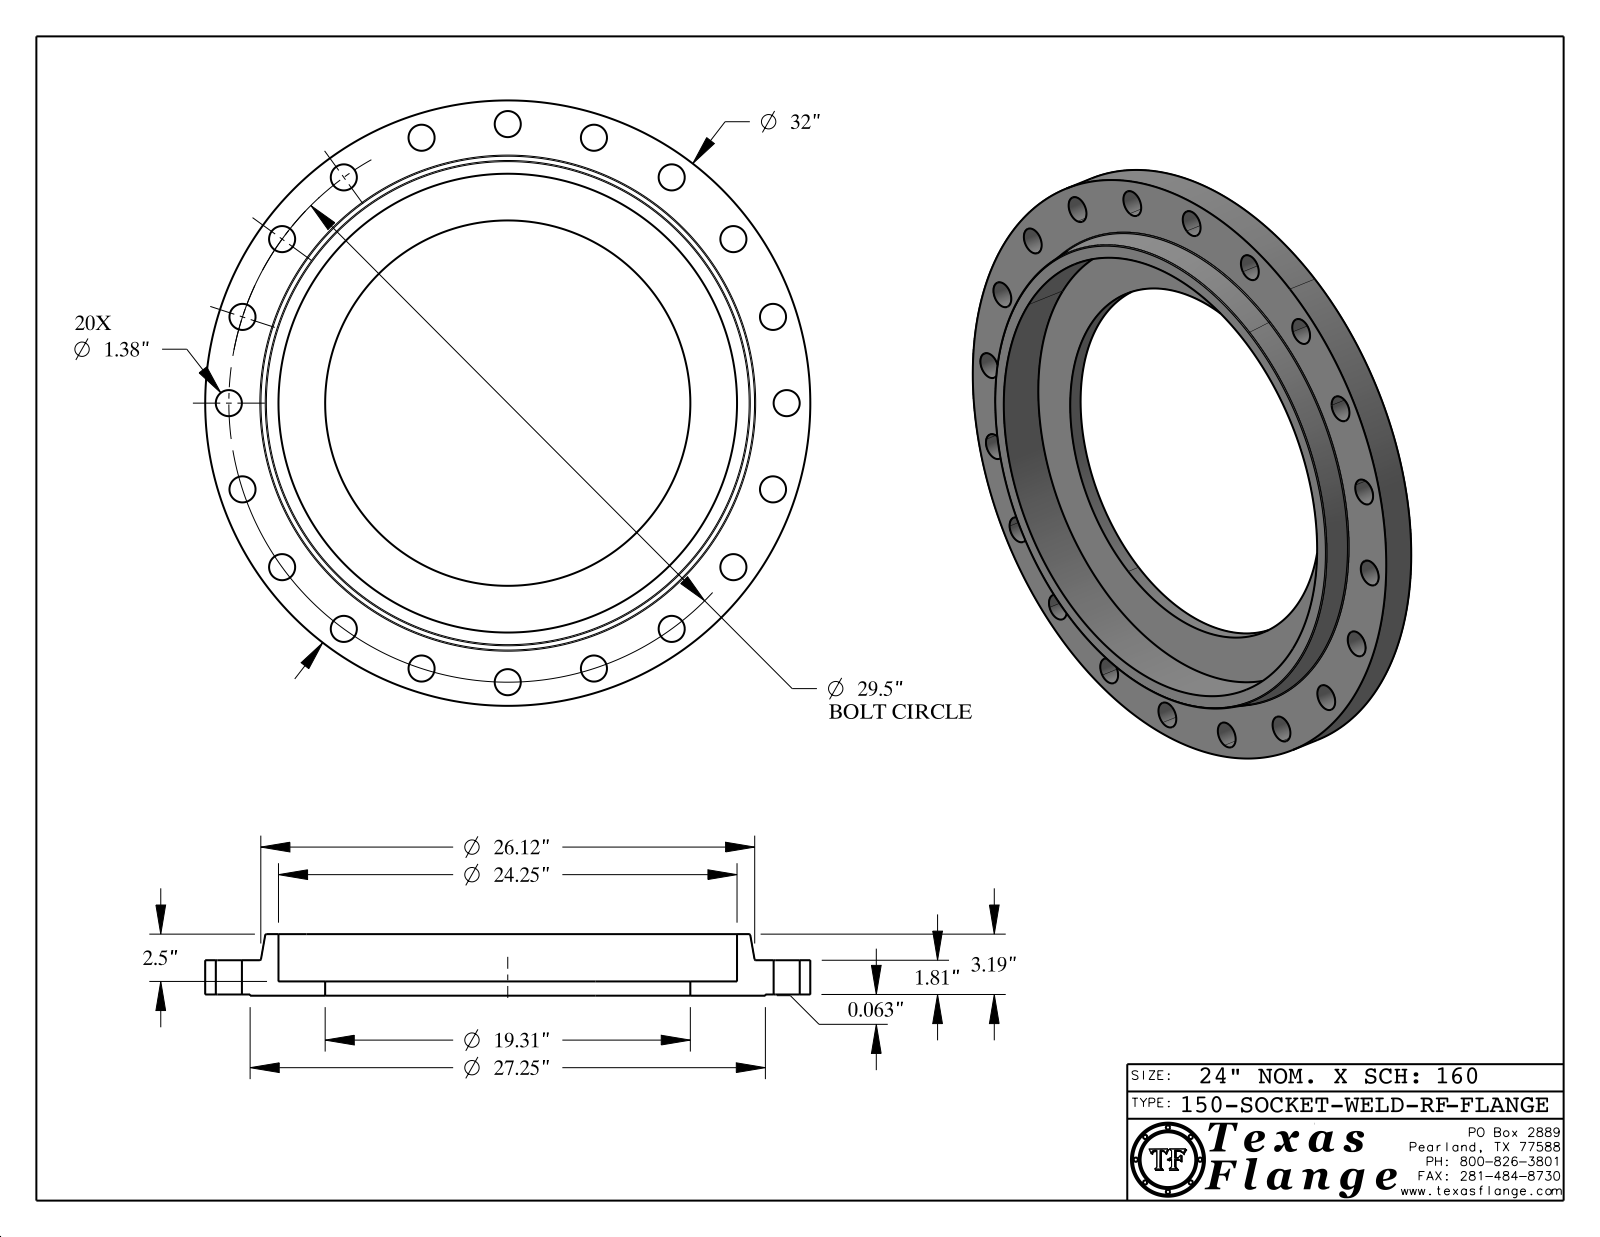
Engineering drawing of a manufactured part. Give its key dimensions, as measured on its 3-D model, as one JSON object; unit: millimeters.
{"part_name": "150-SOCKET-WELD-RF", "step_written_by": "CATIA V5 STEP AP214 (AUTOMOTIVE_DESIGN)", "units": "millimeters", "bodies": {"solids": 1, "faces": 444, "planar": 370, "cylindrical": 68, "other": 6}, "overall_size": [812.8, 812.8, 82.6], "volume_mm3": 12920000, "surface_area_mm2": 1055000, "round_holes": [[35.1, 20], [12.6, 1], [490.5, 1], [616, 1]], "round_bosses_or_shafts": [[0.8, 8], [812.8, 1], [692.2, 1], [9.9, 1]], "face_to_face_distances": [47.5, 1.6, 46, 19.1, 17.5, 28.4, 82.6, 81, 63.5, 35.1], "hole_center_spacings": [374.7, 740.1, 117.2, 440.4, 529.8, 606.2, 667.6, 231.5]}
